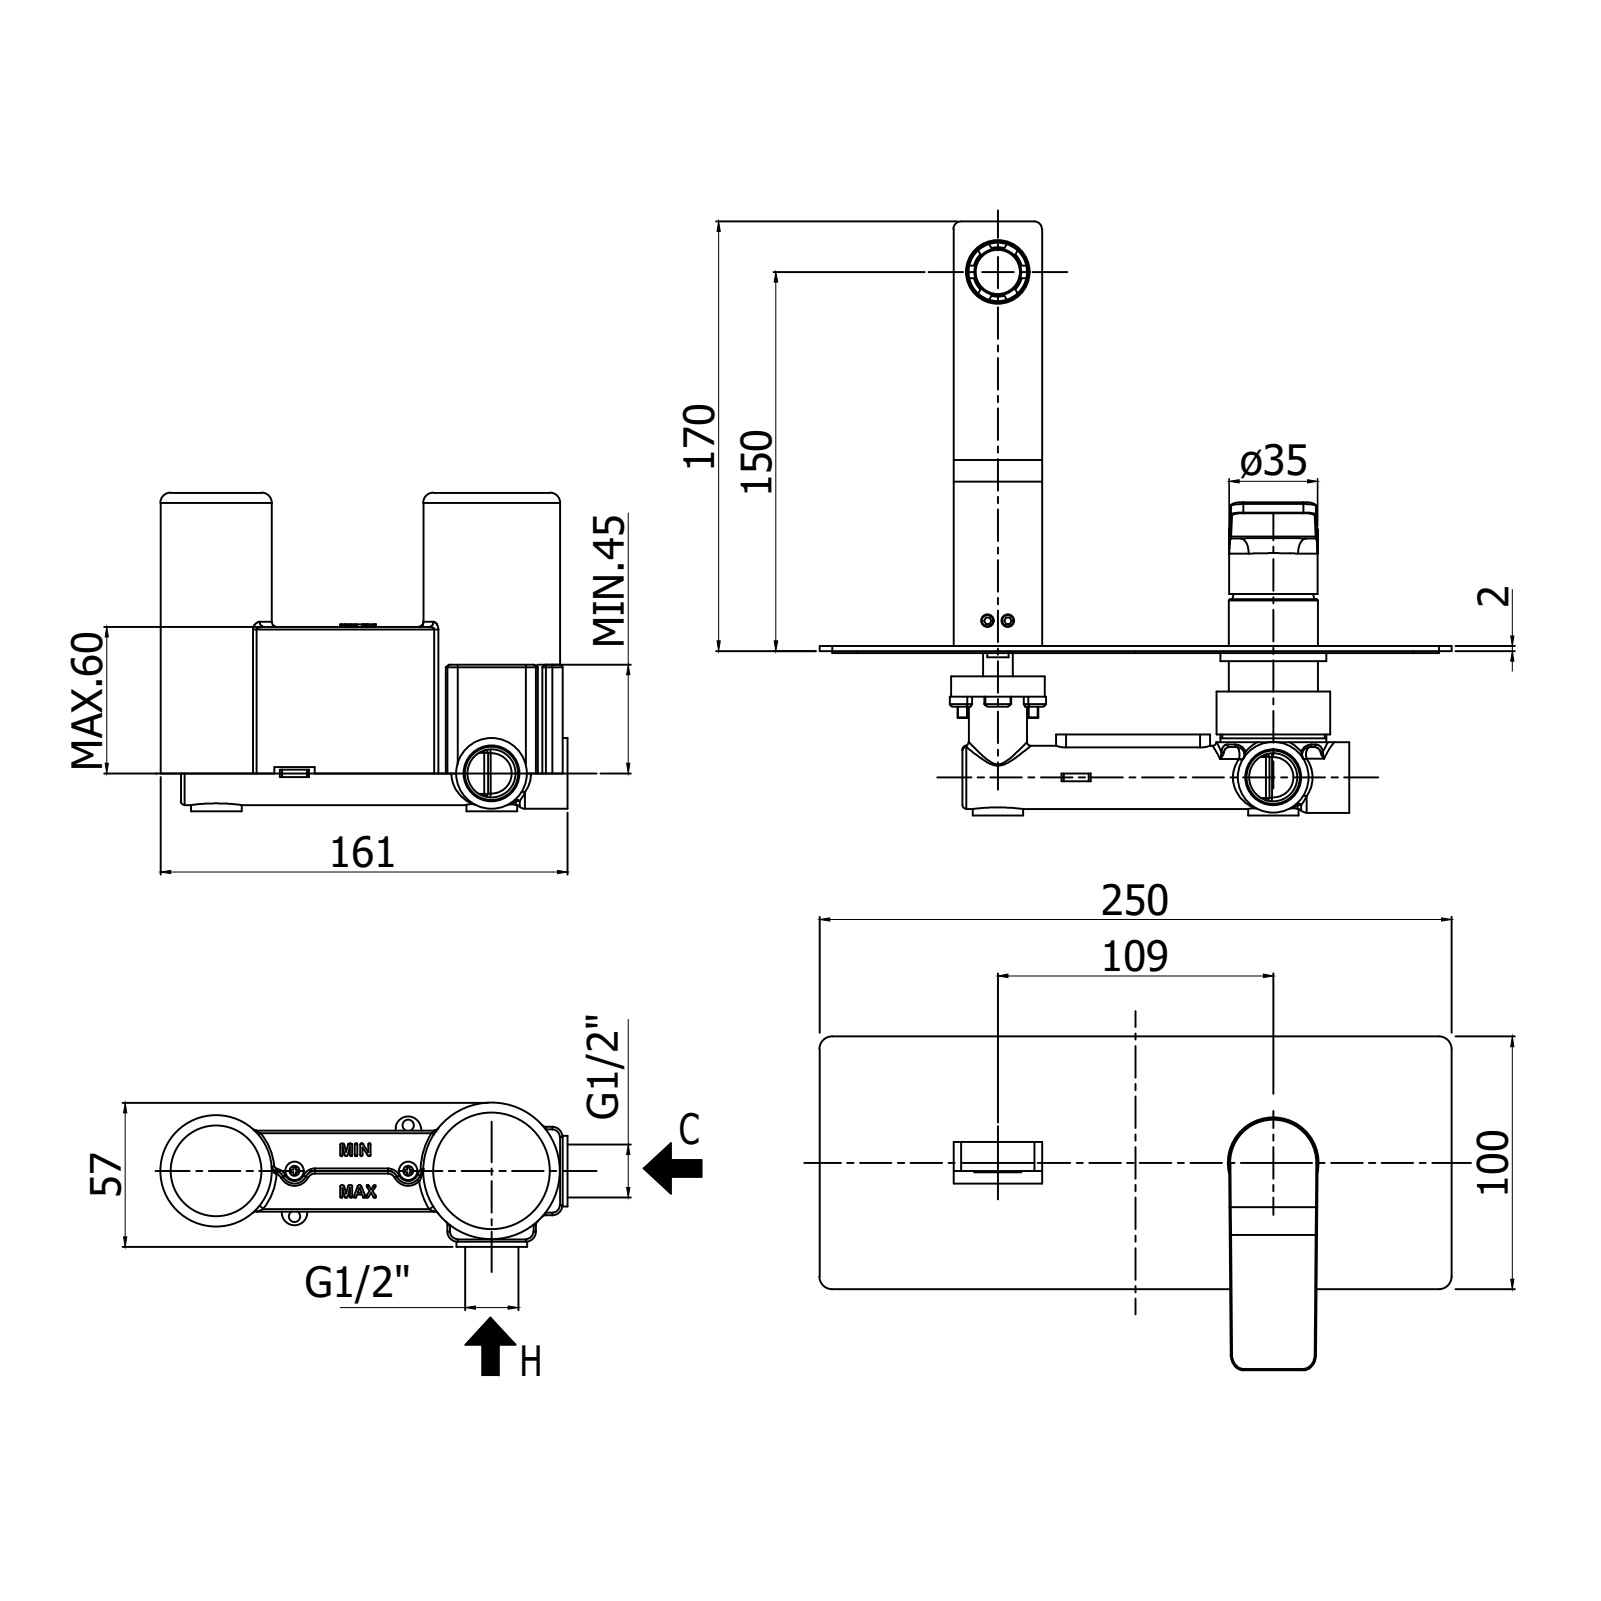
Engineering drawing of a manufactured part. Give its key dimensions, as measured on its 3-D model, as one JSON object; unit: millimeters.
{"part_name": "TI104CR", "step_written_by": "CREO PARAMETRIC BY PTC INC, 2020044 (CONFIG_CONTROL_DESIGN)", "units": "millimeters", "bodies": {"solids": 2, "faces": 198, "planar": 68, "cylindrical": 77, "other": 53}, "overall_size": [250, 170, 132.1], "volume_mm3": 153536, "surface_area_mm2": 86316, "round_holes": [[3, 1], [4.2, 1], [24.8, 1], [26.2, 1], [27, 1], [28, 1], [29, 1], [30.6, 1], [31.7, 1]], "round_bosses_or_shafts": [[35.2, 1], [35, 1], [18.5, 1], [7.6, 1], [5.5, 1]], "partial_cylinders_radius": [[0.5, 12], [1, 8], [3, 6], [5, 6], [1.5, 2], [3.5, 1], [44.14, 1], [63, 1]], "face_to_face_distances": [2, 11.5, 5, 16.5, 35, 4.02, 46.6, 48.6, 41.75, 58.25]}
